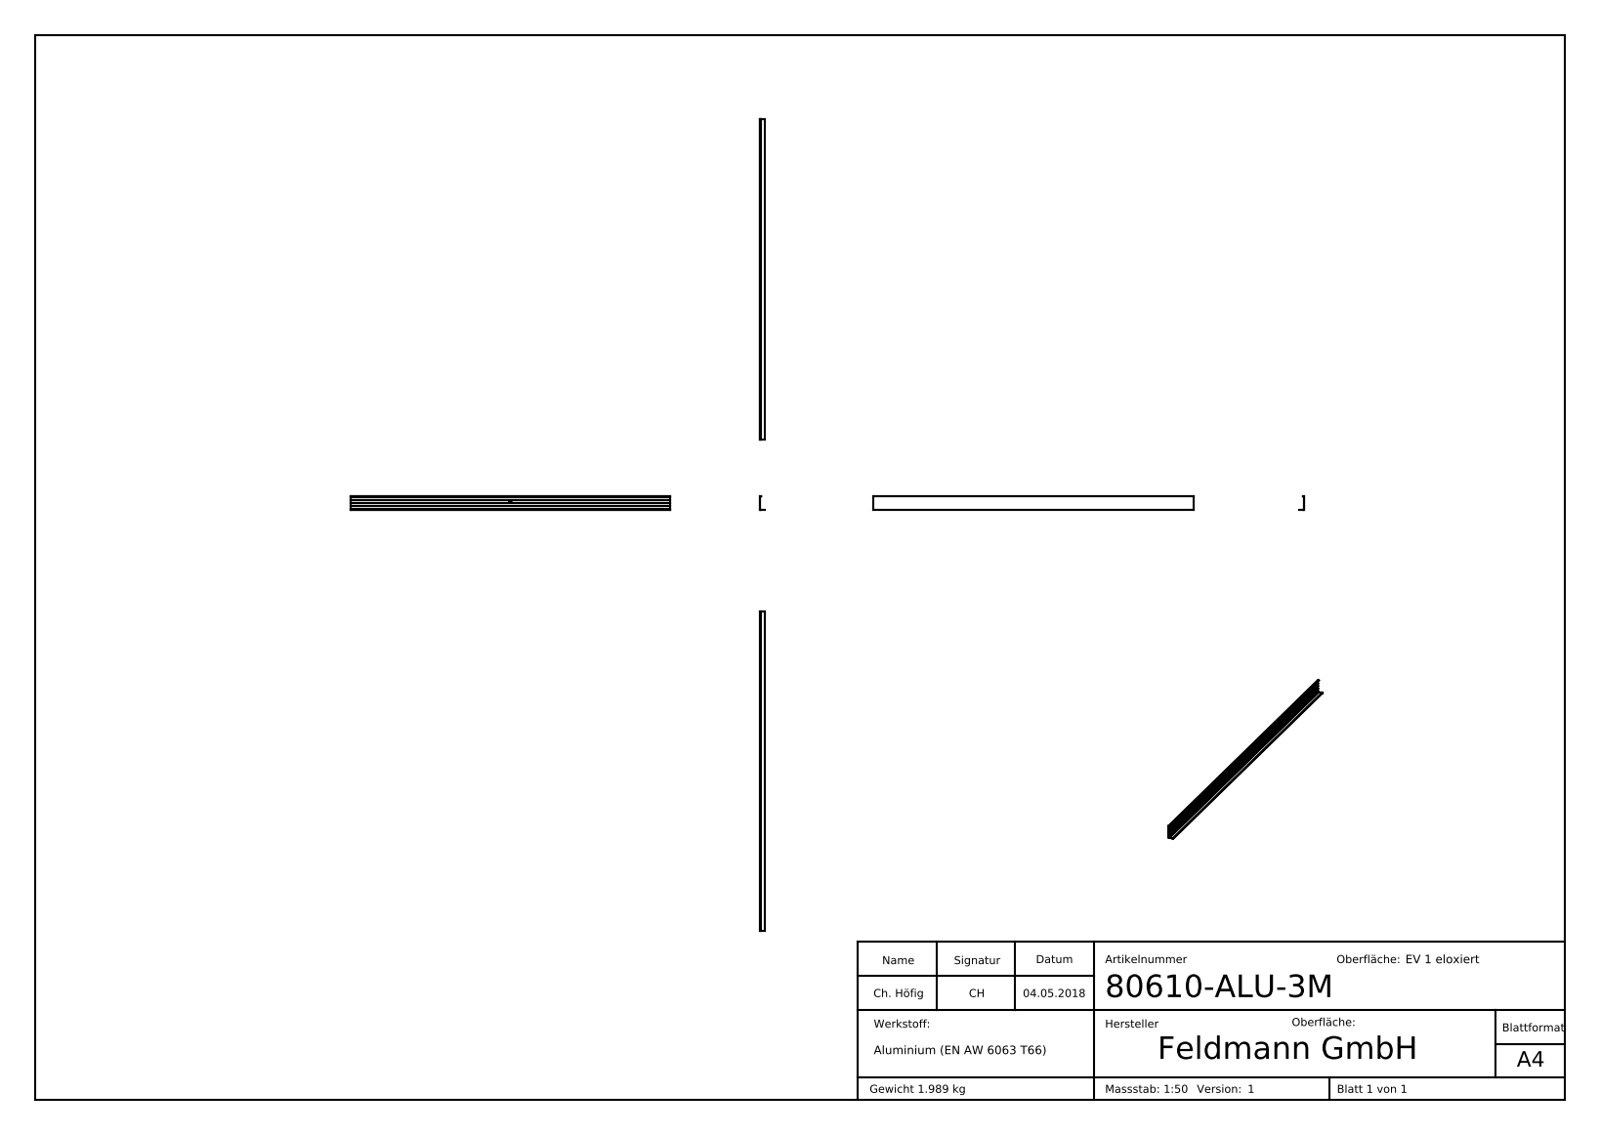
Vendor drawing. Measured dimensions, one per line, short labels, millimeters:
name: 80610-ALU-3M
written by: SolidWorks 2015 (CONFIG_CONTROL_DESIGN)
unit: mm
bodies: 1 solid, 296 faces (176 planar, 7 cylindrical, 113 other)
size: 3000 × 128.5 × 47.9
volume: 736 488 mm³; area: 1 114 000 mm²
rounds: 2× R0.3, 2× R1.2, 1× R1.7, 1× R2, 1× R2.2
face distances: 1.3, 1.5, 128.5, 127.2, 127, 10.2, 28.5, 8.9, 8.7, 47.9
